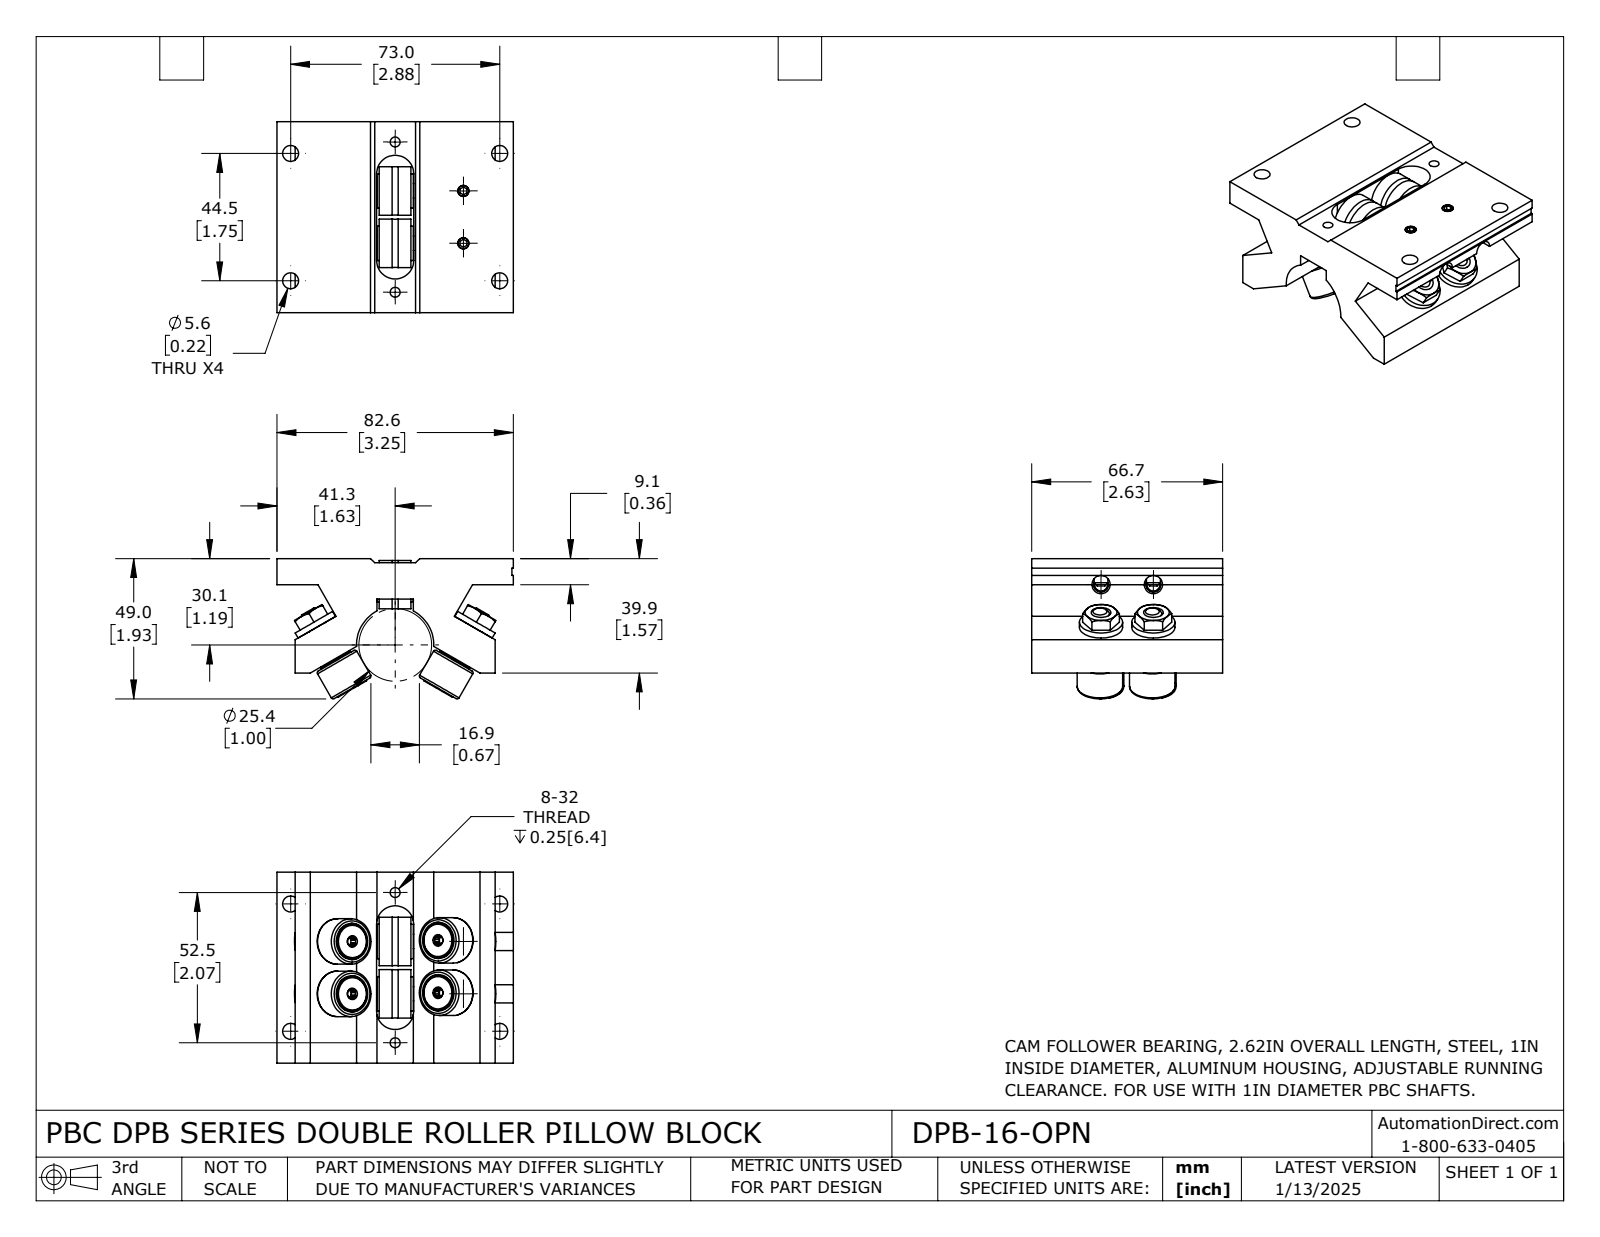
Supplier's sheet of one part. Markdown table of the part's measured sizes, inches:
| quantity | value |
| --- | --- |
| part name | DPB-16-OPN |
| STEP written by | SolidWorks 2023 (CONFIG_CONTROL_DESIGN) |
| units | inches |
| bodies | 16 solids, 517 faces (211 planar, 158 cylindrical, 148 other) |
| overall size | 3.25 × 2.625 × 1.928 |
| volume | 7.803 in³ |
| surface area | 62.72 in² |
| round holes (diameter × count) | 0.129 × 4, 0.204 × 4, 0.219 × 4, 0.499 × 4, 0.136 × 2, 0.15 × 2, 0.156 × 2, 0.197 × 2, 0.25 × 2, 0.253 × 2, 0.26 × 2, 0.377 × 2 |
| round bosses / shafts (diameter × count) | 0.469 × 5, 0.625 × 4, 0.594 × 4, 0.666 × 2, 0.472 × 2, 0.405 × 2, 0.26 × 2, 0.255 × 2 |
| partial cylindrical surfaces (radius × count) | 0.255 × 2, 0.531 × 1 |
| main face-to-face distances | 0.5, 2.625, 0.36, 0.25, 3, 1.12, 1.63, 1.88, 1.37, 2.75 |
| hole center spacings | 0.72, 1.446, 2.389, 0.015, 0.717, 1.154, 1.679, 2.431 |
